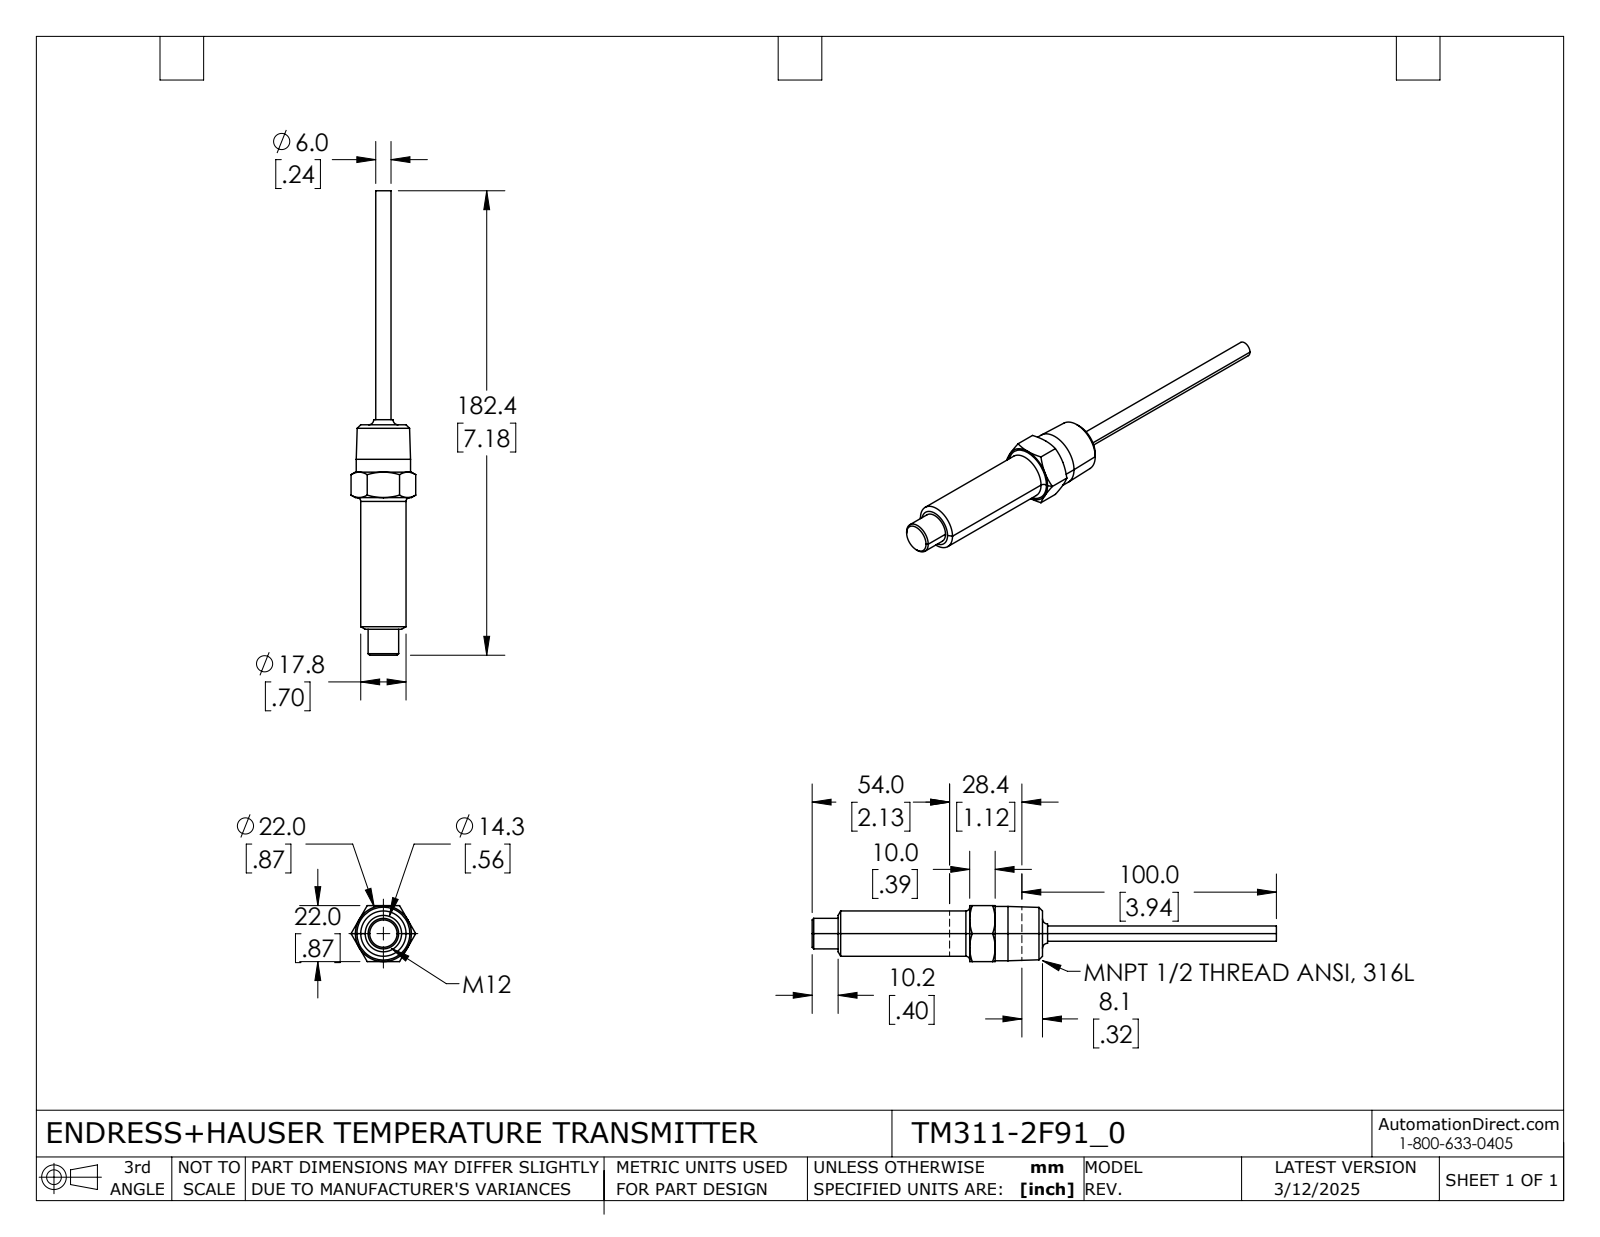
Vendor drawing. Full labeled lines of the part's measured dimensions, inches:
Part name (STEP PRODUCT): TM311-2F91_0
STEP written by: SolidWorks 2021 (AUTOMOTIVE_DESIGN)
Units: inches
Bodies: 1 solid, 49 faces (13 planar, 8 cylindrical, 28 other)
Overall size (bounding box): 7.181 × 1 × 0.866
Volume: 1.661 in³ · Surface area: 11.81 in²
Round bosses / shafts (diameter × count): ⌀0.84 ×1, ⌀0.701 ×1, ⌀0.472 ×1, ⌀0.236 ×1
Main face-to-face distances: 0.866, 3.563, 3.161, 0.402, 1.126, 2.035, 2.437, 3.618, 4.744, 6.78
